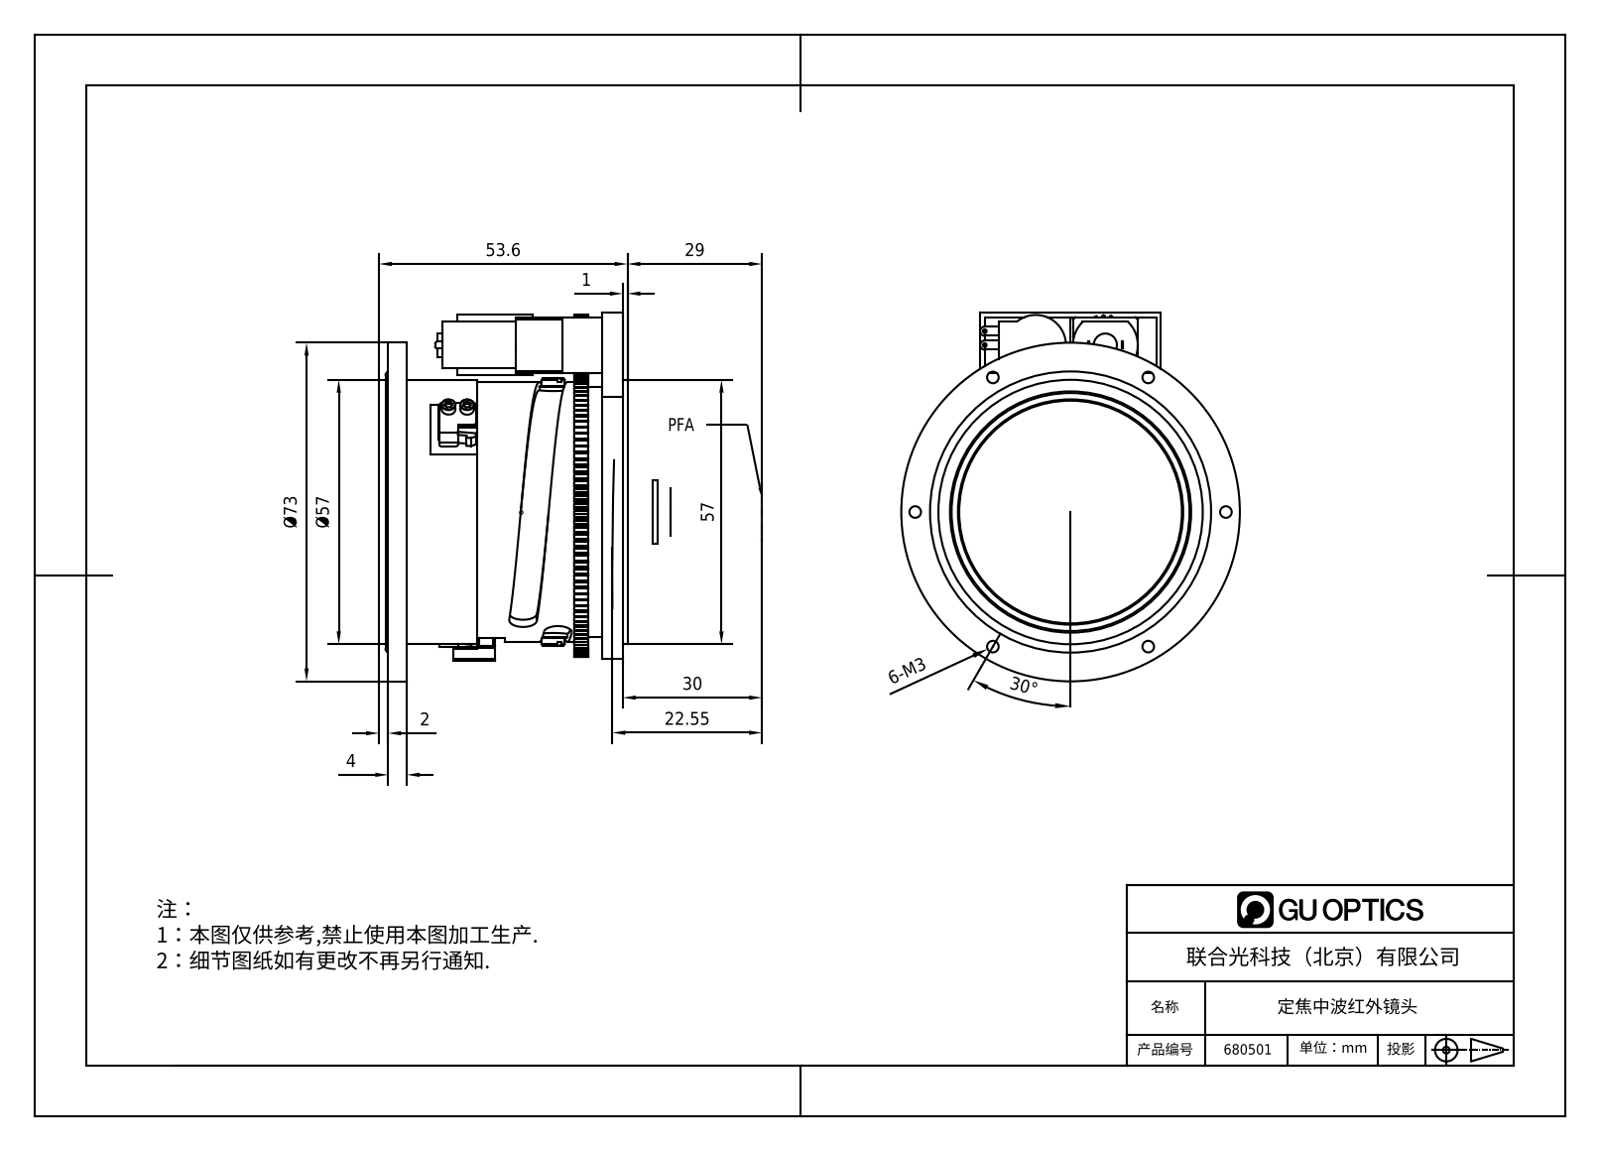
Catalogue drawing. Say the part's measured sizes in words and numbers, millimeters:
The part is named "LB-0031-350F2中波制冷电动镜头外形图-20210826". Its 3-D file was written by "SolidWorks 2020 (CONFIG_CONTROL_DESIGN)". It is 13 solids with 1320 faces: 328 planar, 591 cylindrical and 401 other. Overall it measures 82.6 by 79.5 by 73 millimeters. Its volume is 136 525 cubic millimeters and its surface area 35 711 square millimeters. Round holes: 10 of diameter 1.8, 8 of diameter 1.25, 6 of diameter 2.5, 4 of diameter 1.6, 4 of diameter 2.05, 2 of diameter 0.4, 2 of diameter 0.8, 2 of diameter 2.2, 2 of diameter 3, 1 of diameter 4, 1 of diameter 8, 1 of diameter 24.2. Round bosses or shafts: 4 of diameter 3, 2 of diameter 10, 2 of diameter 6, 2 of diameter 5, 2 of diameter 3.5, 2 of diameter 2, 2 of diameter 1.6, 1 of diameter 73. Partial cylindrical surfaces (rounded edges, fillets, slot ends): 96 of radius 0.19, 24 of radius 0.5, 8 of radius 0.3, 2 of radius 0.8, 2 of radius 0.9, 2 of radius 1, 2 of radius 1.1, 2 of radius 1.6. The main face-to-face distances are 1, 4, 3, 42.1, 5.5, 51.6, 6, 8.5, 50.6, 46.6. The hole center spacings are 23.5, 33.5, 29.79, 49.61, 10, 40.7, 57, 58.02.
